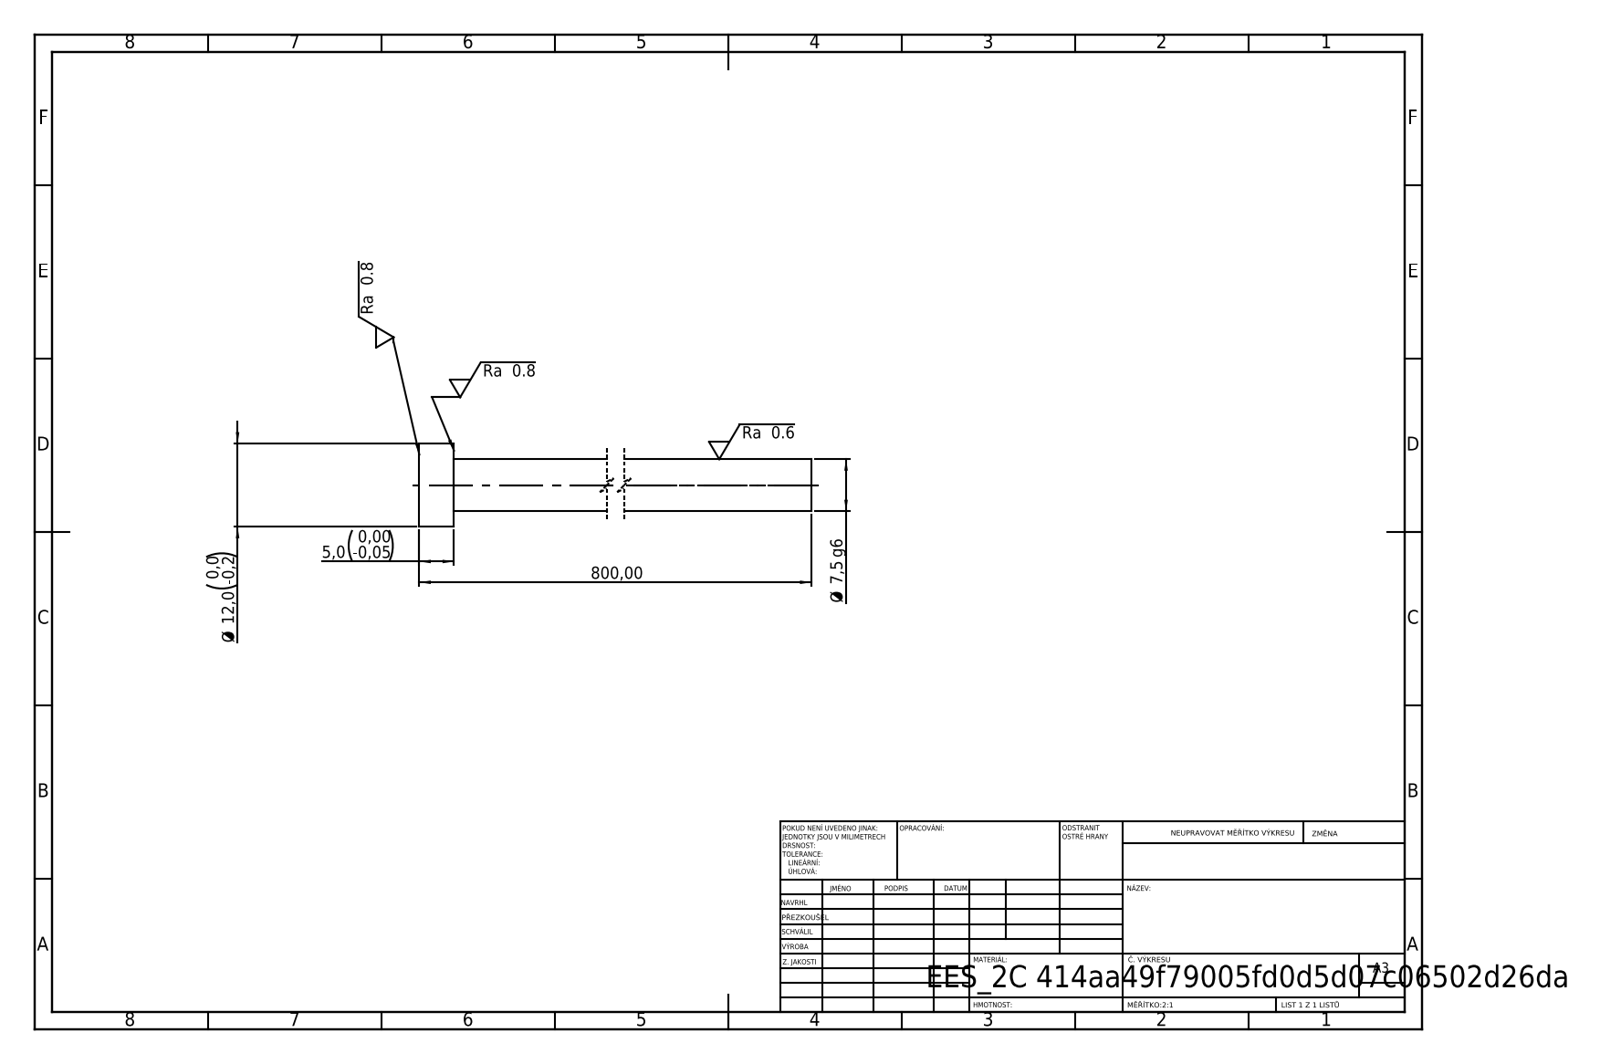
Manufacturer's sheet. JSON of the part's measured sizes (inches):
{"step_written_by": "SolidWorks 2019 (CONFIG_CONTROL_DESIGN)", "units": "inches", "bodies": {"solids": 1, "faces": 7, "planar": 3, "cylindrical": 4, "other": 0}, "overall_size": [31.496, 0.472, 0.472], "volume_in3": 2.178, "surface_area_in2": 29.68, "round_bosses_or_shafts": [[0.472, 1], [0.295, 1]], "face_to_face_distances": [0.197, 31.496, 31.299]}
